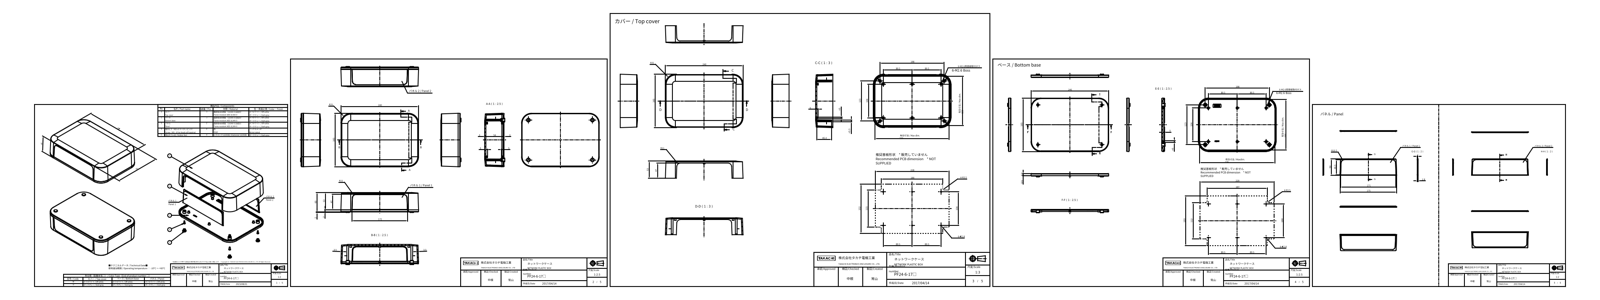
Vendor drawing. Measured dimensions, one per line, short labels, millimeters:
name: PF24-6-17; PFB24-17; PFC24-6-17; PFP24-6 (+3 more)
written by: Autodesk Inventor 2013 (AUTOMOTIVE_DESIGN)
unit: mm
bodies: 12 solids, 1437 faces (720 planar, 209 cylindrical, 508 other)
size: 240 × 165 × 62
volume: 353 584 mm³; area: 256 333 mm²
holes: 6× ⌀2, 6× ⌀6.5, 4× ⌀2.5, 4× ⌀3.5, 4× ⌀7.5, 2× ⌀6
bosses: 4× ⌀3, 1× ⌀2.32
rounds: 56× R0.1, 32× R0.6, 16× R0.5, 8× R1, 8× R2, 4× R0.3, 4× R0.54, 4× R0.64
face distances: 3, 57, 60, 54, 2, 3.5, 3.31, 3.28, 0.8, 4
hole spacings: 13.44, 89.5, 99.45, 113.9, 137.21, 150.61, 188.74, 220.03
